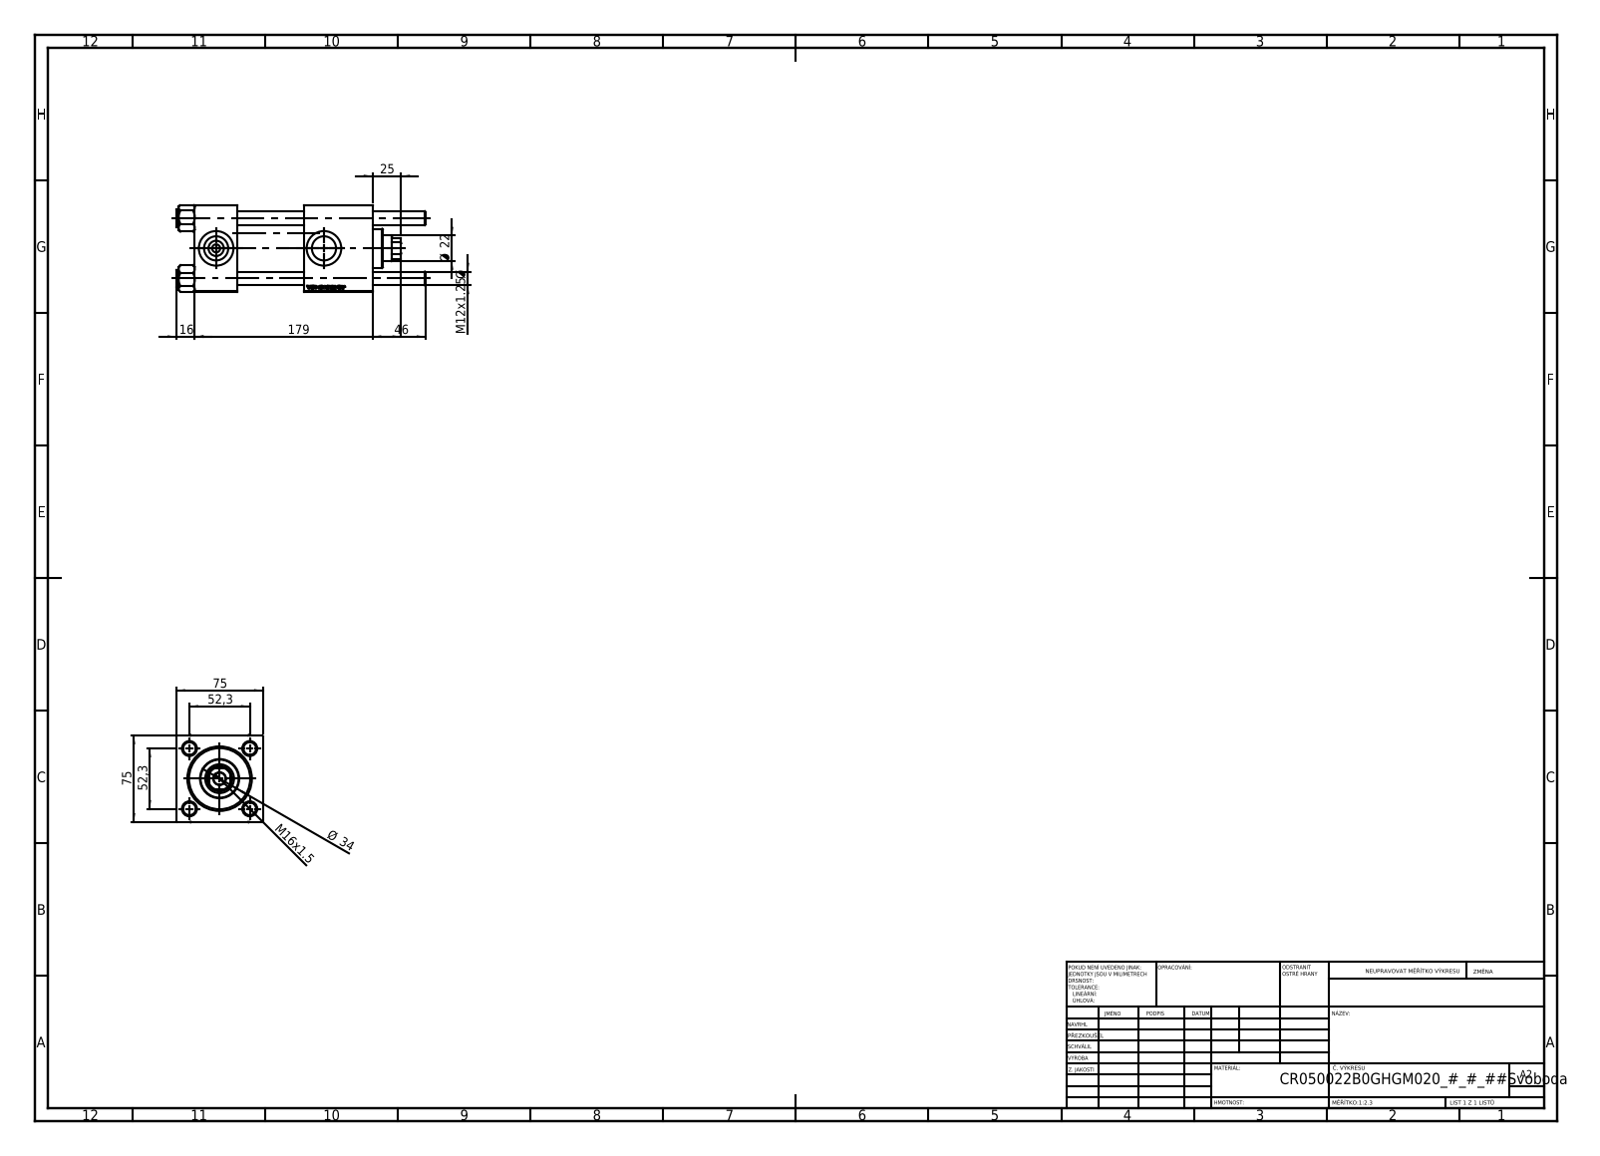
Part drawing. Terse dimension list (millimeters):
name: V215CR_VCP_B; V215_VC_A; V215CR_B-1; NUT_M5_B (+1 more)
written by: SolidWorks 2019 (CONFIG_CONTROL_DESIGN)
unit: mm
bodies: 11 solids, 1158 faces (432 planar, 78 cylindrical, 648 other)
size: 216 × 75.45 × 75
volume: 690 149 mm³; area: 163 490 mm²
holes: 4× ⌀12, 2× ⌀7, 2× ⌀20.96, 2× ⌀30, 1× ⌀10.5, 1× ⌀22, 1× ⌀25, 1× ⌀41, 1× ⌀50, 1× ⌀53
bosses: 4× ⌀15, 1× ⌀56, 1× ⌀34
rounds: 1× R10.5
face distances: 75, 37, 154, 117, 95, 58, 59, 125.3, 88.3, 30.3
hole spacings: 36.98, 52.3, 73.96, 93.5
